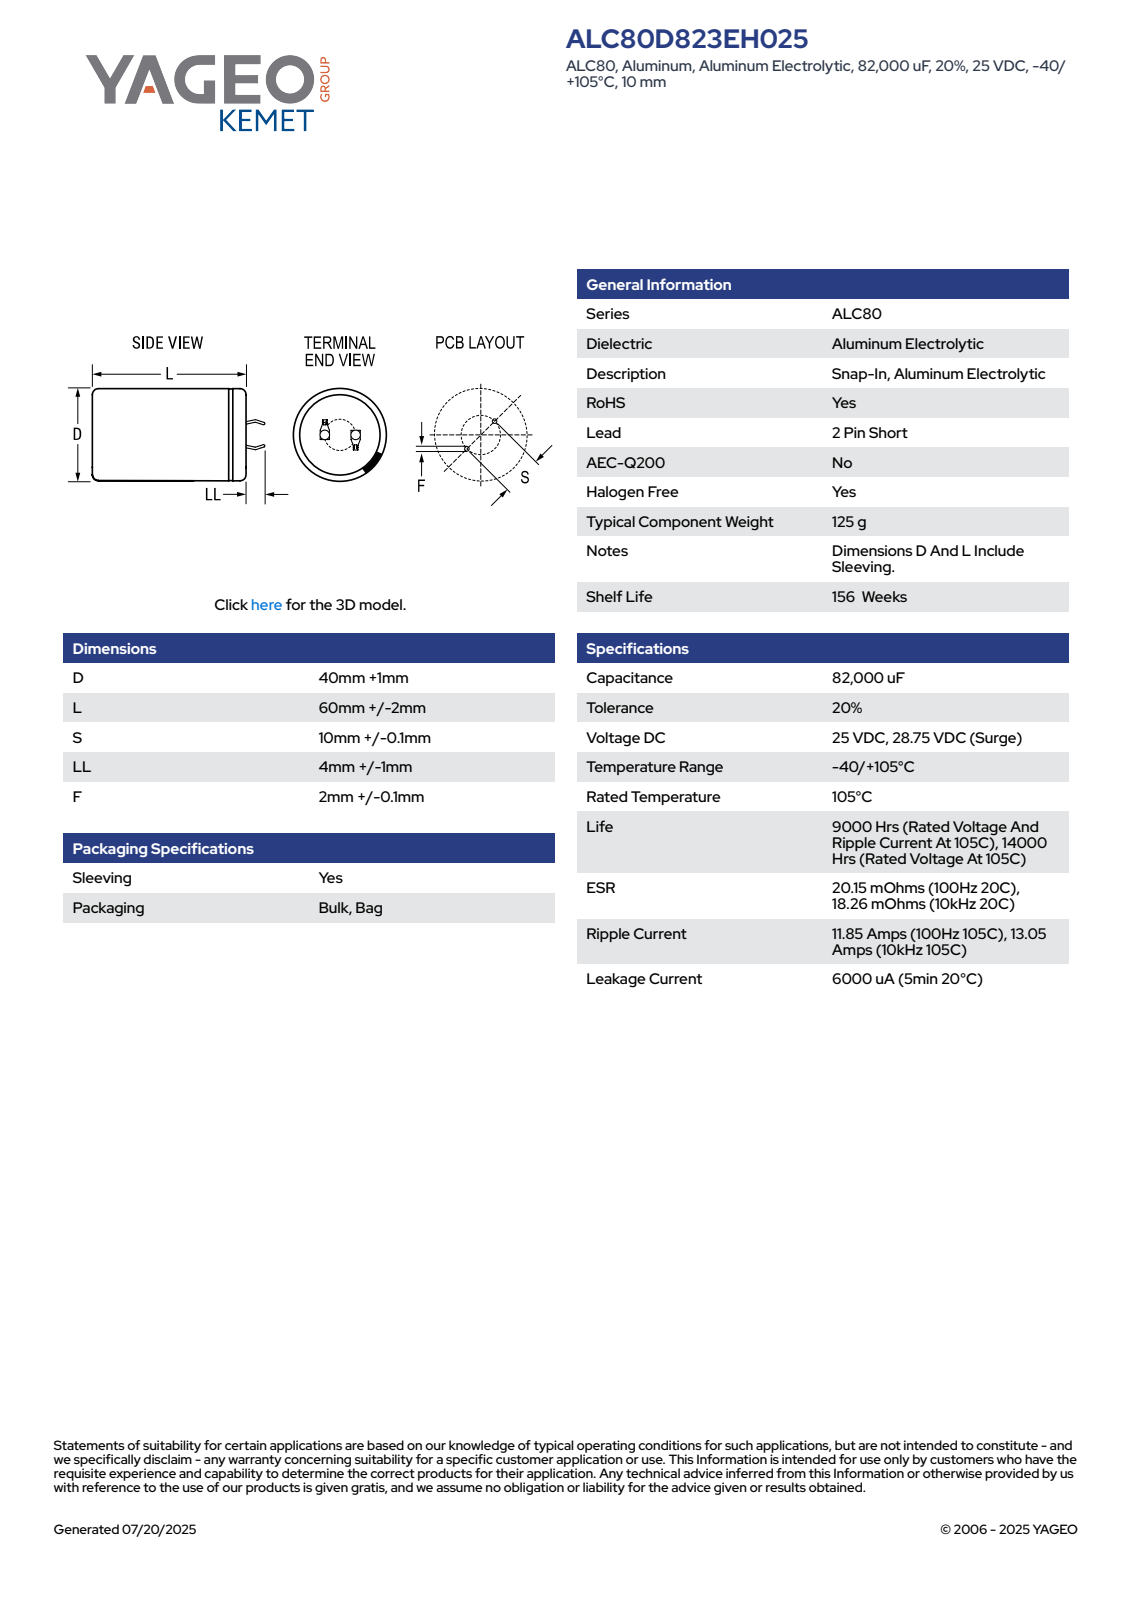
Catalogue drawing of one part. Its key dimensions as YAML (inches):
part_name: "CARS_K2P_40X60_D41L62S10LL5F2.1"
step_written_by: "SolidWorks 2014 (AUTOMOTIVE_DESIGN)"
units: inches
bodies: {solids: 1, faces: 100, planar: 52, cylindrical: 9, other: 39}
overall_size: [2.637, 1.614, 1.614]
volume: 4.947
surface_area: 16.43
round_holes:
  - {diameter: 1.428, count: 1}
round_bosses_or_shafts:
  - {diameter: 1.614, count: 1}
partial_cylinders:
  - {radius: 0.807, count: 1}
face_to_face_distances: [2.441, 2.46, 0.02, 0.279, 0.024, 0.023, 0.299, 0.03, 0.053, 0.302]
